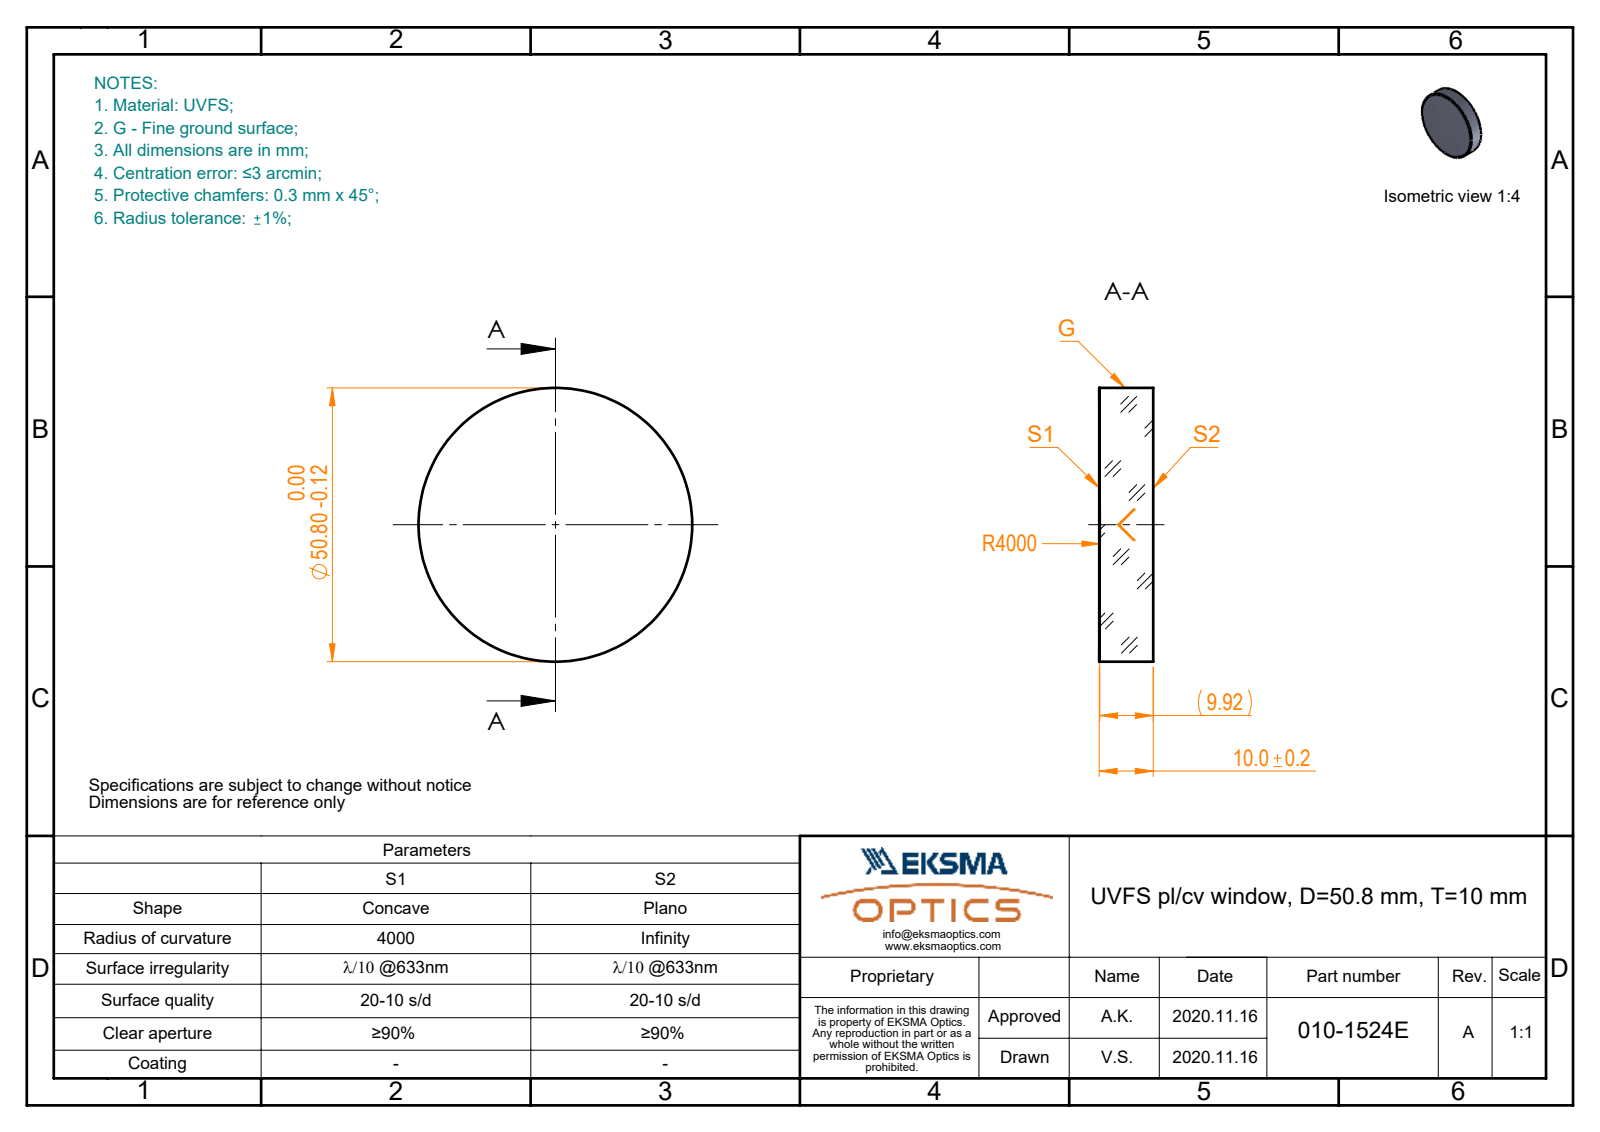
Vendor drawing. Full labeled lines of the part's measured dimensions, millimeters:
Part name (STEP PRODUCT): 010-1524E_UVFS_PCV_window
STEP written by: SolidWorks 2019 (CONFIG_CONTROL_DESIGN)
Units: millimetres
Bodies: 1 solid, 5 faces (1 planar, 2 cylindrical, 2 other)
Overall size (bounding box): 50.8 × 50.8 × 10
Volume: 20 187 mm³ · Surface area: 5 650 mm²
Round bosses / shafts (diameter × count): ⌀50.8 ×1
